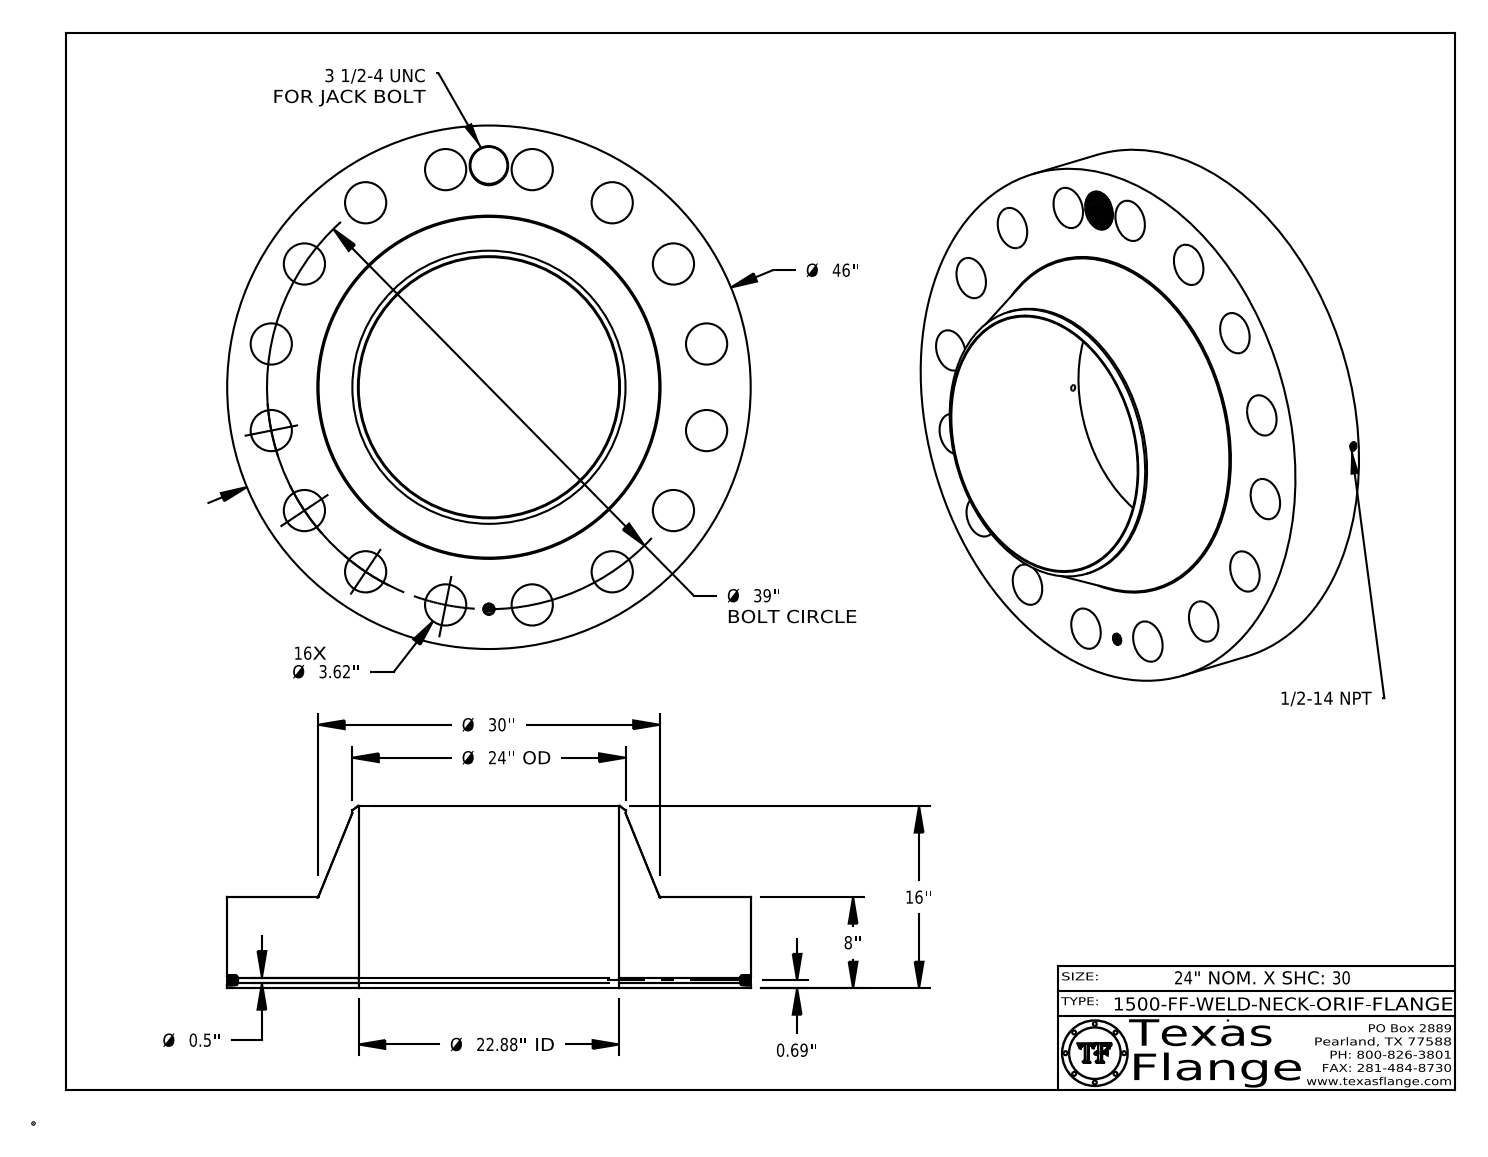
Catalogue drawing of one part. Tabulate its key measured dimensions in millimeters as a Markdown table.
| quantity | value |
| --- | --- |
| part name | 1500-FF-WELD-NECK |
| STEP written by | CATIA V5 STEP AP214 (AUTOMOTIVE_DESIGN) |
| units | millimeters |
| bodies | 1 solid, 884 faces (368 planar, 142 cylindrical, 374 other) |
| overall size | 1168.4 × 1168.4 × 406.4 |
| volume | 161 300 000 mm³ |
| surface area | 4 209 000 mm² |
| round holes (diameter × count) | 91.9 × 16, 12.7 × 1, 17.1 × 1, 25.4 × 1, 82.6 × 1, 581.1 × 1 |
| round bosses / shafts (diameter × count) | 1.5 × 8, 1168.4 × 1, 609.6 × 1, 20 × 1 |
| main face-to-face distances | 203.2, 406.4, 202.8, 0.4, 203.6, 7.6, 7.4, 1.4, 6.3, 4.9 |
| hole center spacings | 495.3, 700.5, 915.2, 823.6, 193.2, 379.1, 379.1, 550.3 |
